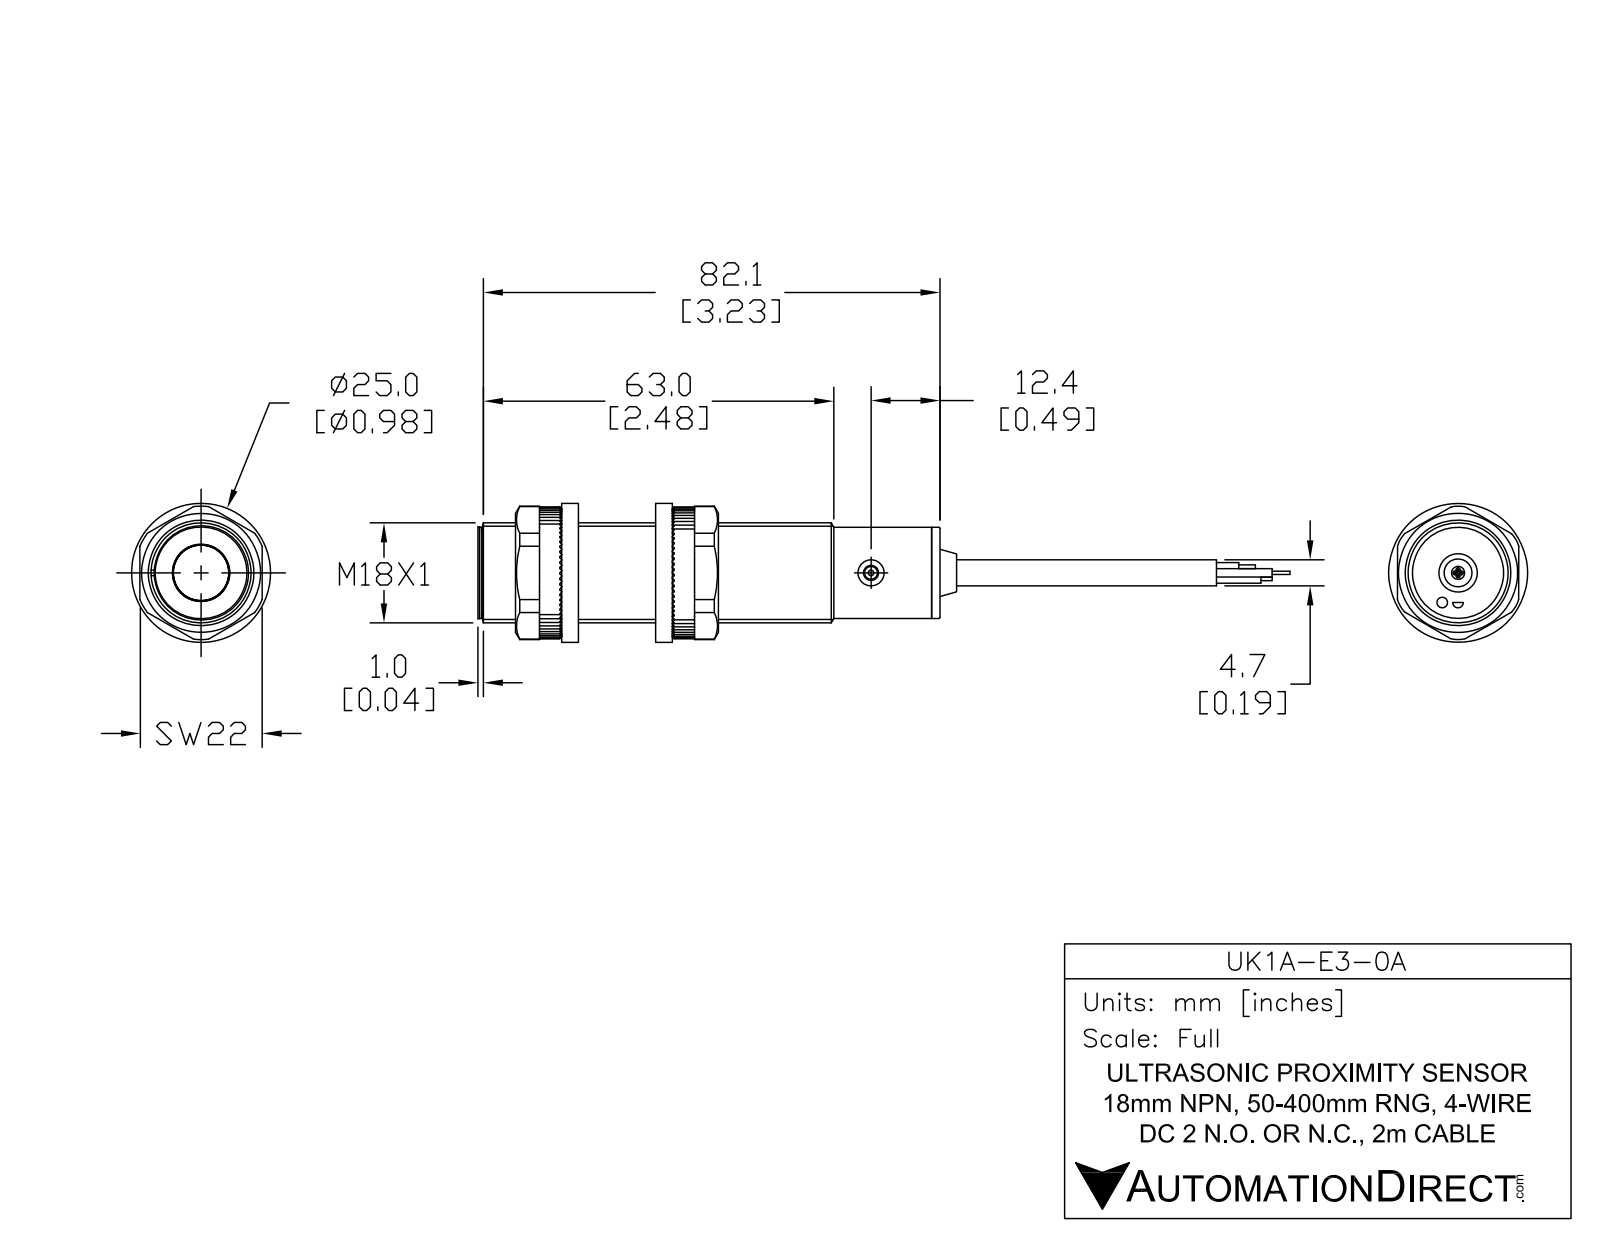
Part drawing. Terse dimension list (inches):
name: UK1A-E3-0A
written by: SolidWorks 2017 (AUTOMOTIVE_DESIGN)
unit: in
bodies: 6 solids, 55 faces (17 planar, 24 cylindrical, 14 other)
size: 4.832 × 0.709 × 0.709
volume: 1.285 in³; area: 10.69 in²
holes: 2× ⌀0.185, 1× ⌀0.106
bosses: 1× ⌀0.709, 1× ⌀0.646, 1× ⌀0.622, 1× ⌀0.374, 1× ⌀0.189, 1× ⌀0.091
face distances: 3.193, 3.252, 0.059, 0.039, 3.232, 3.291, 0.041, 3.234, 3.293, 3.257
